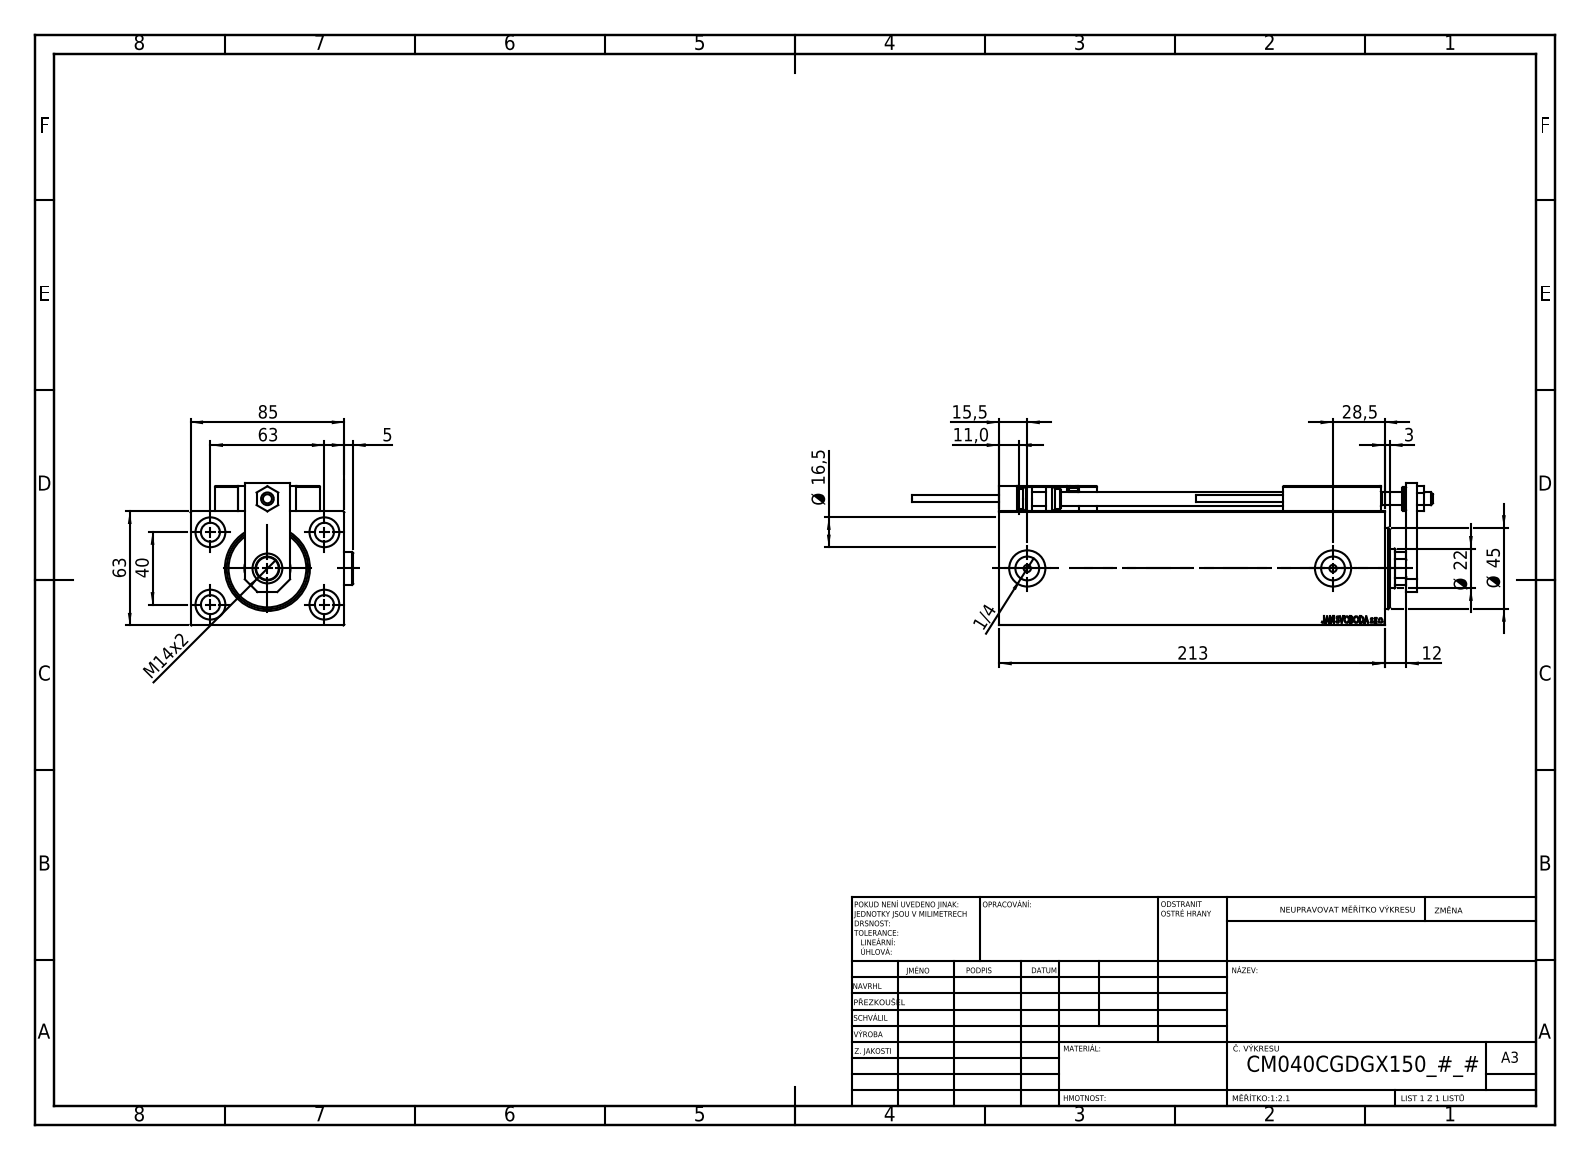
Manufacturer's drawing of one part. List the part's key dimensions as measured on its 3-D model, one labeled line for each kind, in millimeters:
Part name (STEP PRODUCT): MAGNET; Zatka_OIL_PORT; SWITCH DIM B,W; SWITCH_X_FRONT_BACK (+7 more)
STEP written by: SolidWorks 2019 (CONFIG_CONTROL_DESIGN)
Units: millimetres
Bodies: 25 solids, 1336 faces (594 planar, 204 cylindrical, 538 other)
Overall size (bounding box): 287.7 × 89.9 × 78.5
Volume: 978 573 mm³ · Surface area: 185 631 mm²
Round holes (diameter × count): ⌀4 ×6, ⌀8 ×5, ⌀16.5 ×5, ⌀3.2 ×4, ⌀10.5 ×4, ⌀5 ×2, ⌀13.16 ×2, ⌀20 ×2, ⌀7 ×1, ⌀12.5 ×1, ⌀22 ×1, ⌀25.5 ×1
Round bosses / shafts (diameter × count): ⌀18 ×2, ⌀5 ×2, ⌀3.8 ×2, ⌀13 ×1, ⌀11 ×1
Partial cylindrical surfaces — rounded edges, fillets, slot ends (radius × count): R0.3 ×30, R3 ×2, R10.5 ×1
Main face-to-face distances: 63, 85, 12, 201, 213, 14, 77, 15, 18, 30
Hole centre spacings: 37.31, 11.37, 20, 29.59, 29.69, 36.06, 36.53, 40
